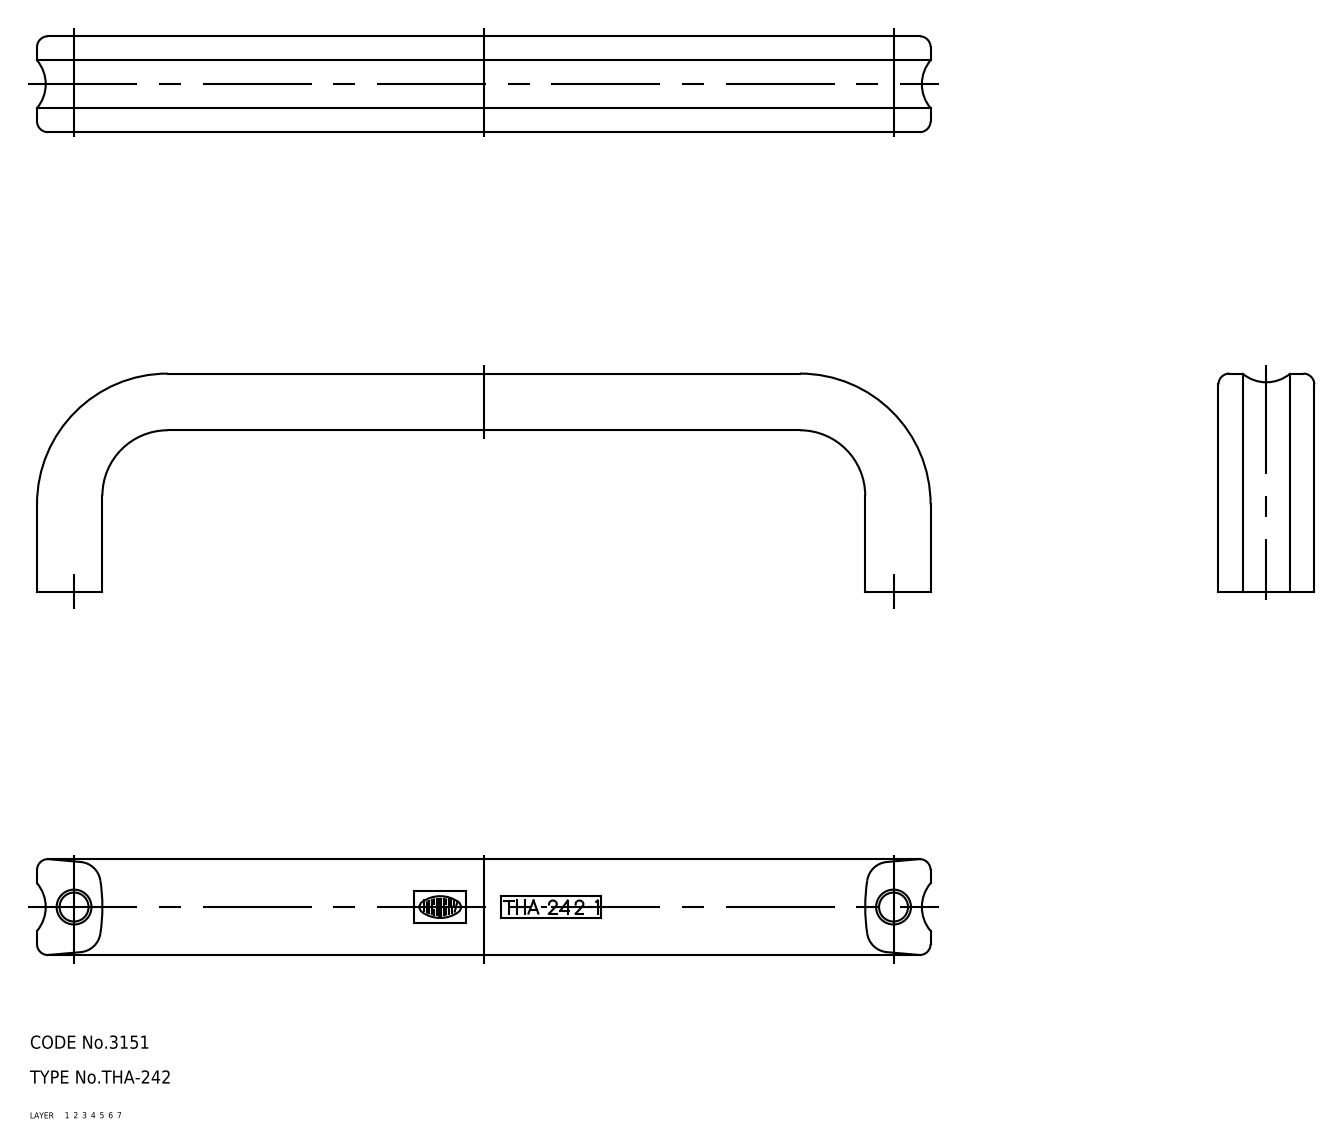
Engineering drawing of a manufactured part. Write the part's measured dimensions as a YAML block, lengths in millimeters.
part_name: "pull"
step_written_by: "CADfix (AUTOMOTIVE_DESIGN)"
units: millimeters
bodies: {solids: 1, faces: 20, planar: 0, cylindrical: 0, other: 20}
overall_size: [205, 50.02, 22]
volume: 65558
surface_area: 17634
